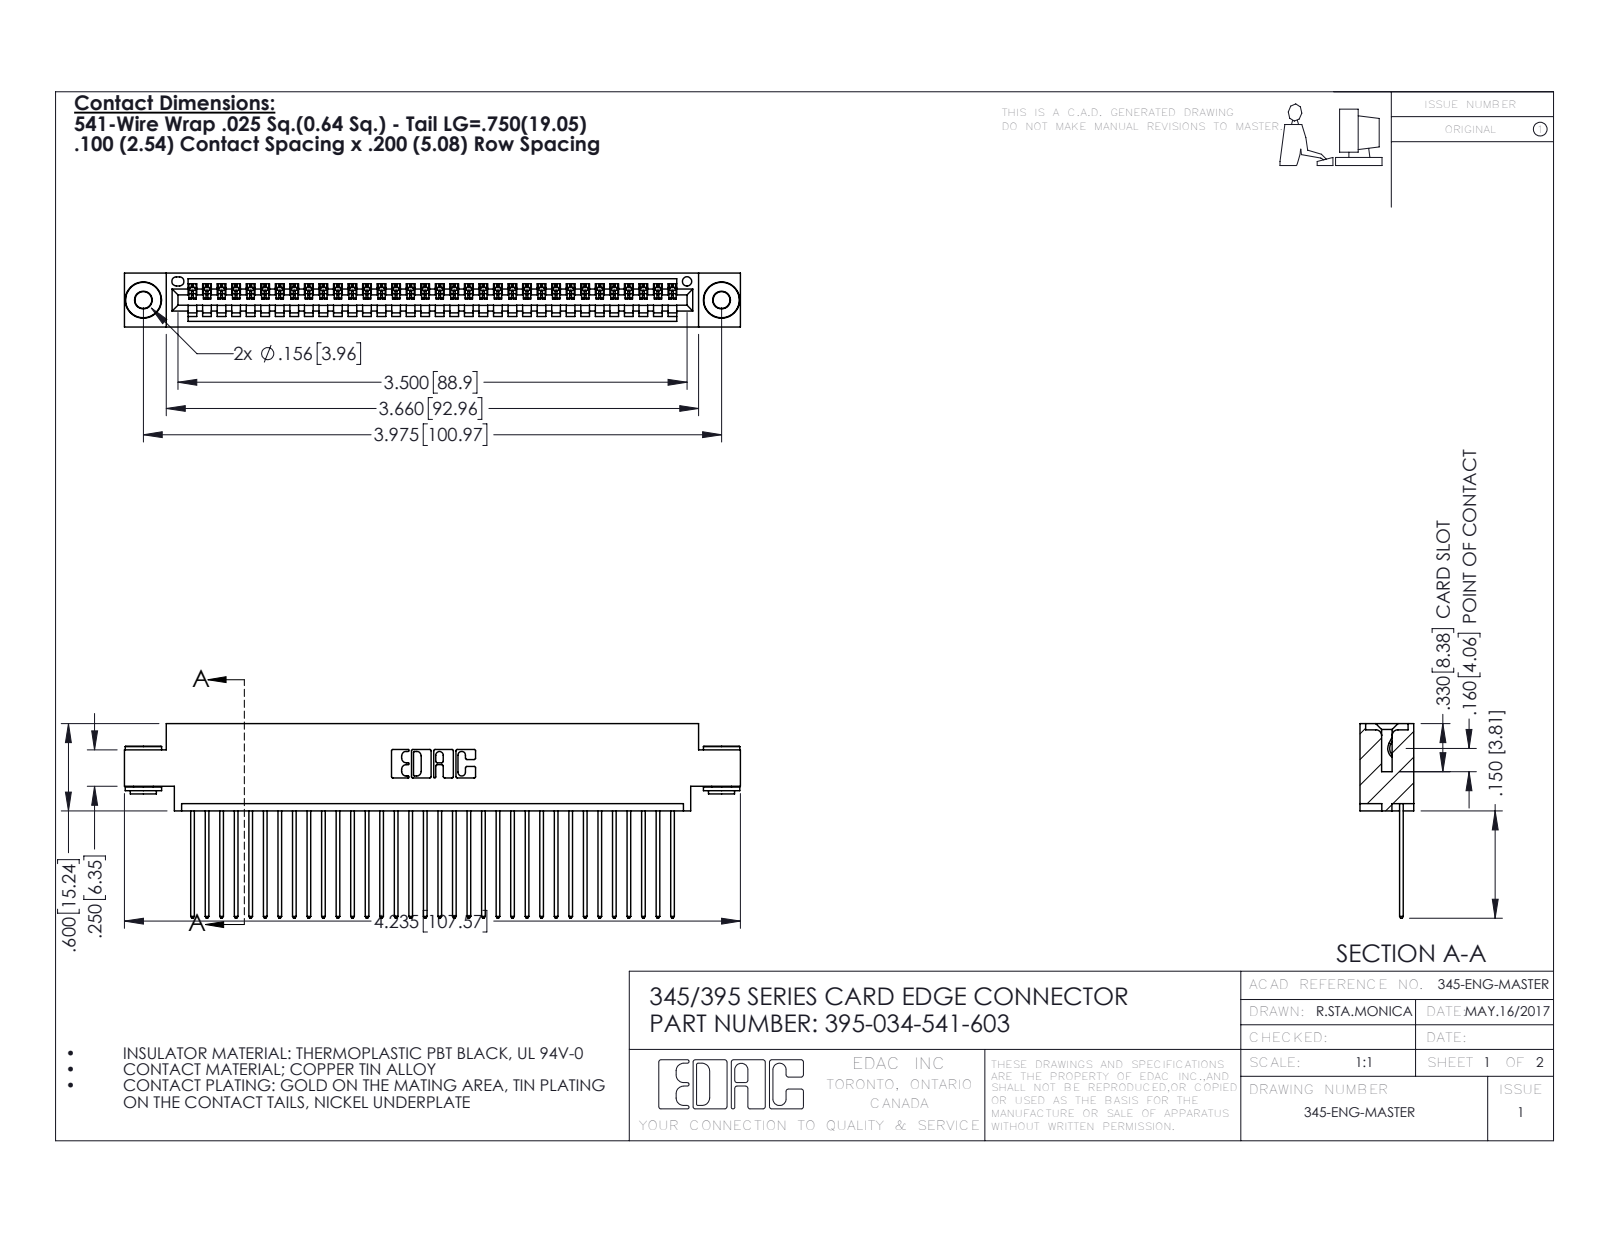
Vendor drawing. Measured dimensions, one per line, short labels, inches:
name: 345 Part_0.170 Offset - 0.156 Dia-TH; 395-034-541-603; 345-250-002_345-250-002-102; 345-292-001_345-293-141
written by: SolidWorks 2016 (CONFIG_CONTROL_DESIGN)
unit: in
bodies: 37 solids, 2140 faces (1454 planar, 678 cylindrical, 8 other)
size: 4.235 × 1.337 × 0.37
volume: 0.621 in³; area: 22.33 in²
holes: 2× ⌀0.116, 2× ⌀0.156, 1× ⌀0.064
bosses: 2× ⌀0.25, 2× ⌀0.18, 2× ⌀0.136
rounds: 68× R0.006, 68× R0.01, 22× R0.01, 6× R0.007, 6× R0.031, 3× R0.026, 2× R0.031, 2× R0.04
face distances: 0.072, 0.298, 0.37, 0.098, 0.272, 0.025, 0.2, 0.225, 0.175, 0.149
hole spacings: 0.27, 3.74, 3.975
